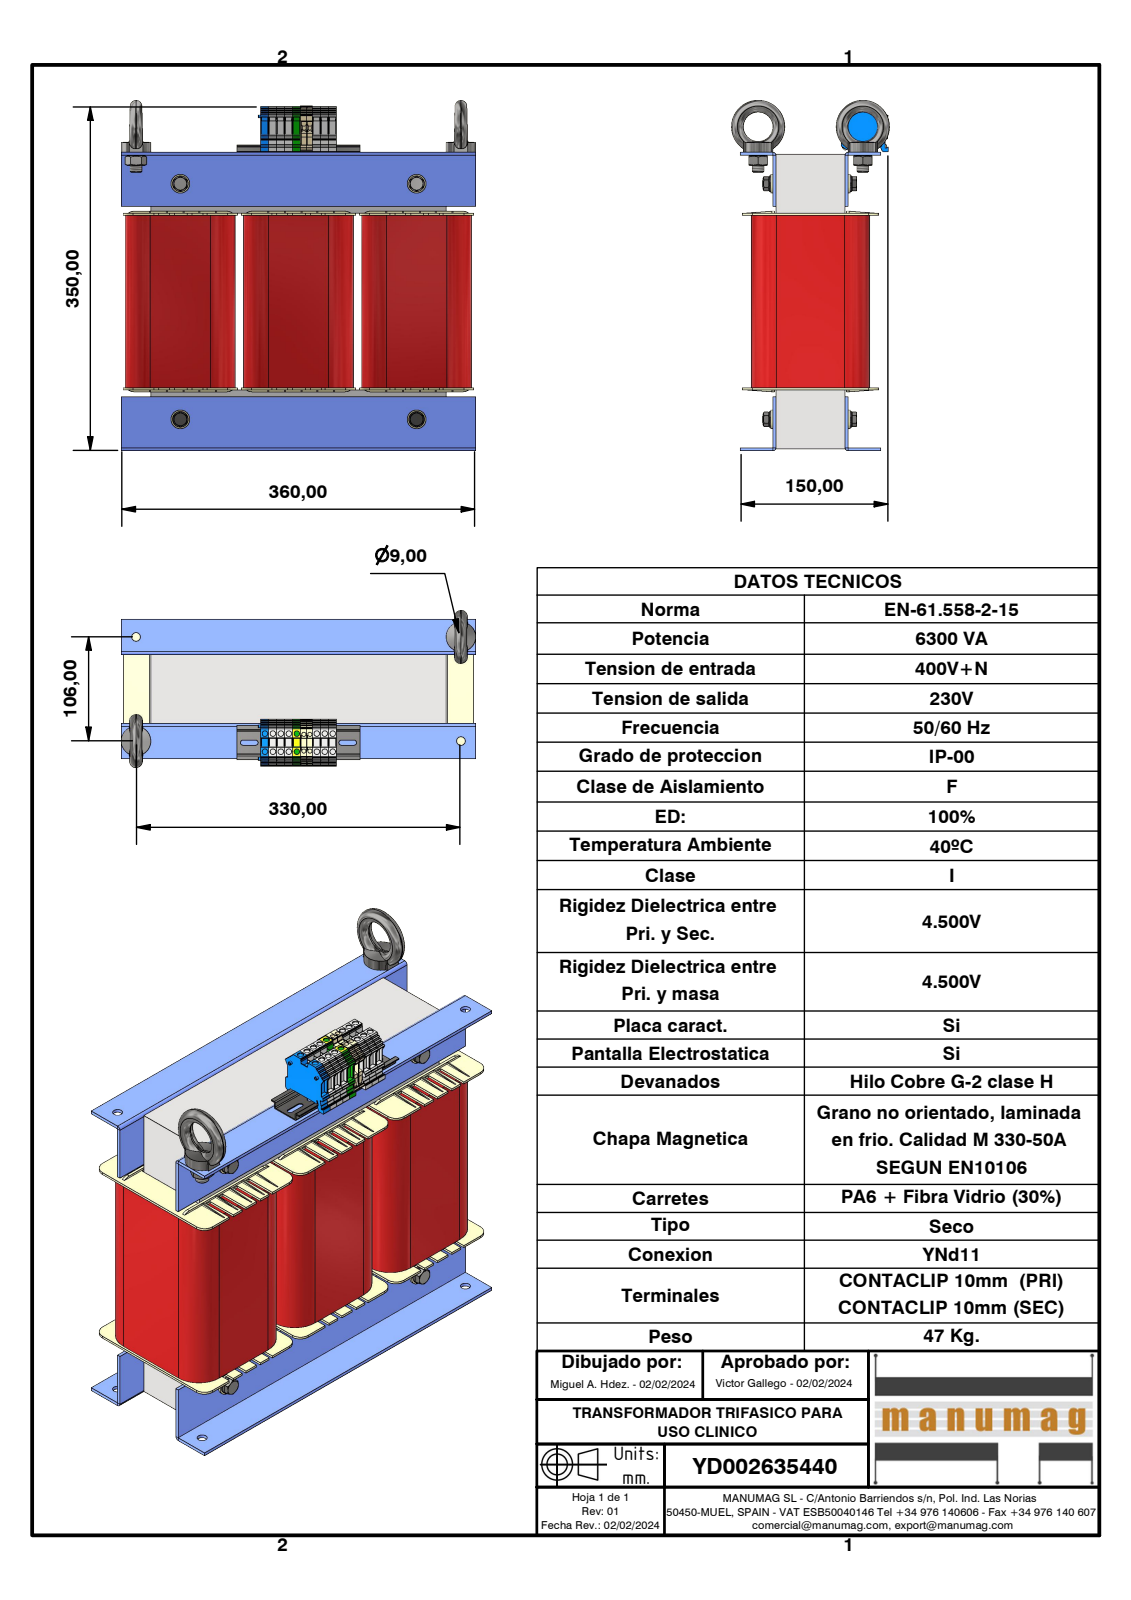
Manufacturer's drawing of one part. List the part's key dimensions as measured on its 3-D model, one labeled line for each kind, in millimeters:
Part name (STEP PRODUCT): YD002635440; UI 180 - 70 (300x300); UI 180_70_BOBINADO; RC60 NT060 (+8 more)
STEP written by: Autodesk Inventor 2023 (AUTOMOTIVE_DESIGN)
Units: millimetres
Bodies: 47 solids, 3890 faces (2788 planar, 886 cylindrical, 216 other)
Overall size (bounding box): 360 × 357 × 160
Volume: 9 692 000 mm³ · Surface area: 1 442 000 mm²
Round holes (diameter × count): ⌀5.7 ×16, ⌀2.4 ×4, ⌀2.5 ×4, ⌀2.75 ×4, ⌀4.3 ×4, ⌀6.65 ×4, ⌀8 ×4, ⌀8.4 ×4, ⌀9 ×4, ⌀10.5 ×4, ⌀11 ×4, ⌀2.95 ×2
Round bosses / shafts (diameter × count): ⌀19 ×4, ⌀16 ×4, ⌀11.4 ×4, ⌀9.6 ×4, ⌀7.32 ×4, ⌀54 ×2, ⌀12 ×2, ⌀10.8 ×2
Partial cylindrical surfaces — rounded edges, fillets, slot ends (radius × count): R0.3 ×86, R1 ×32, R10 ×25, R2 ×18, R0.25 ×17, R3 ×12, R3.31 ×12, R25.37 ×12
Main face-to-face distances: 2.5, 1, 240, 1.5, 3, 73, 60, 70, 120, 22.06
Hole centre spacings: 8.1, 20.1, 16.2, 18.4, 24.52, 36.5, 40.88, 44.6
